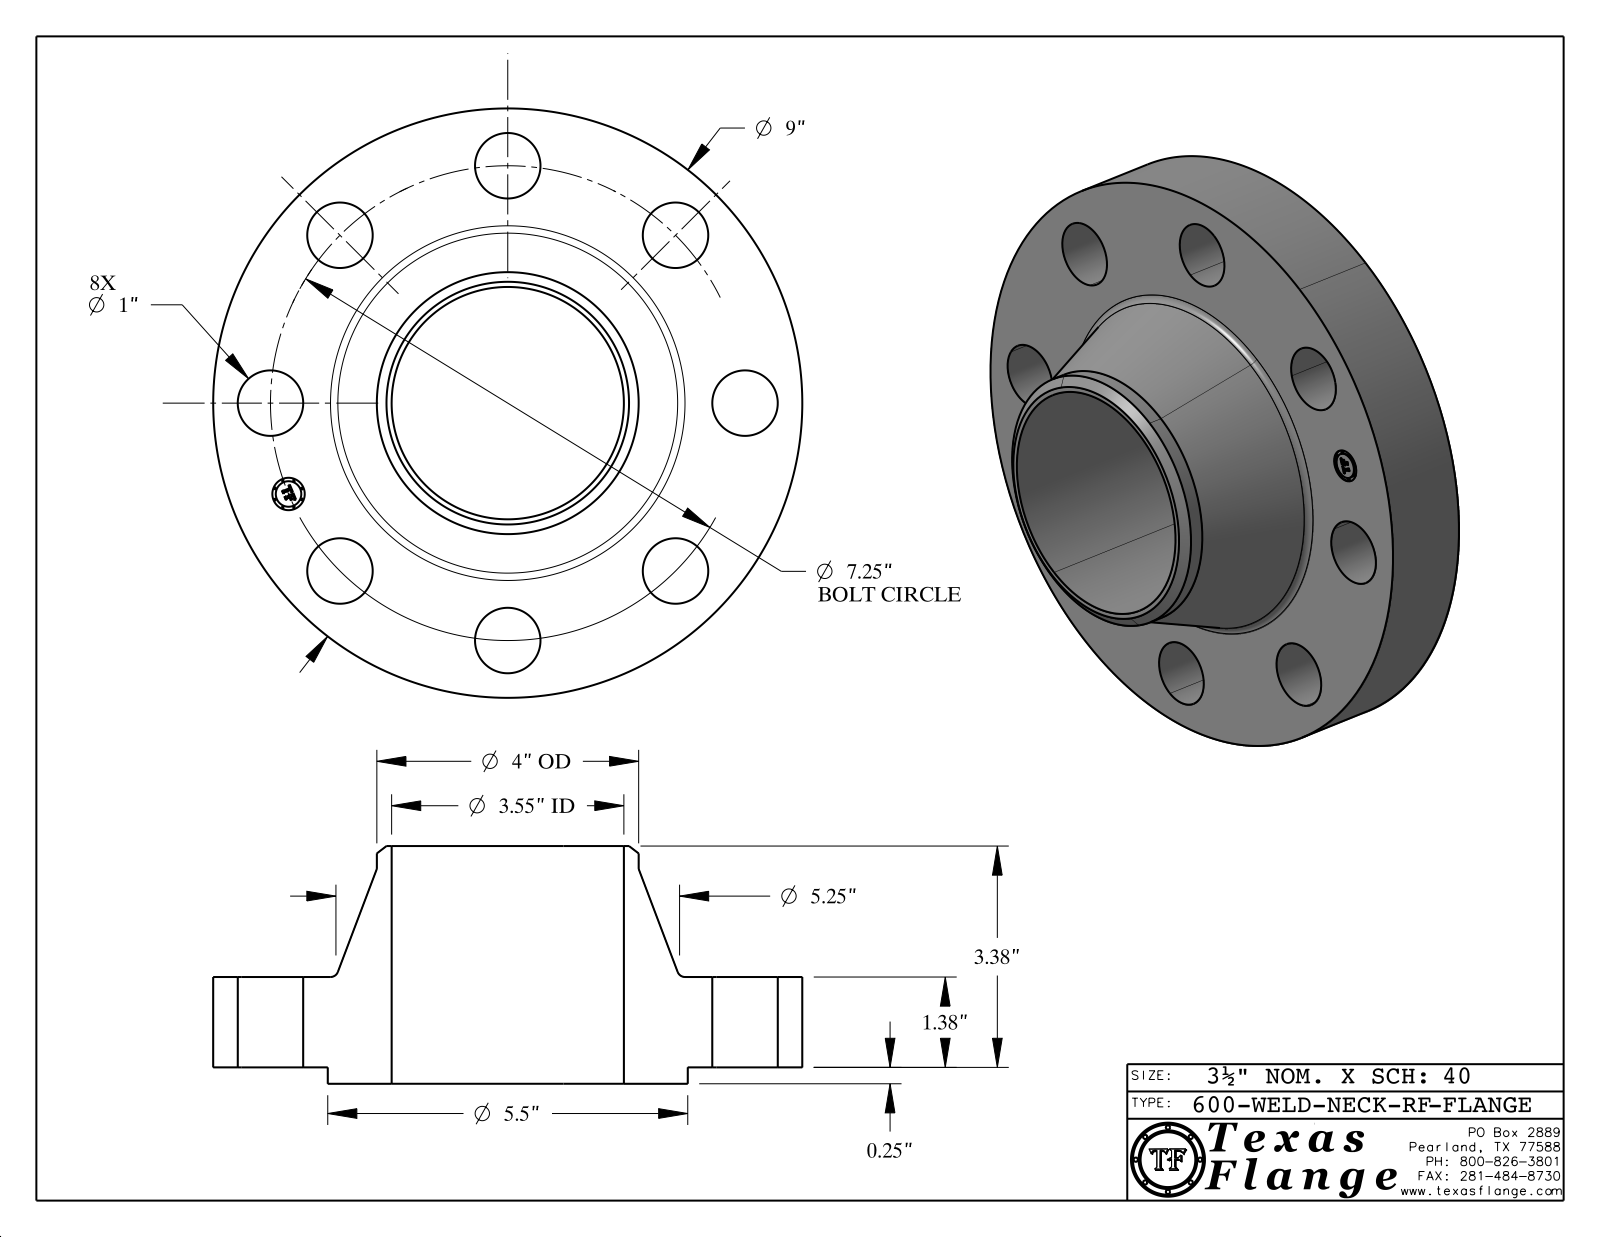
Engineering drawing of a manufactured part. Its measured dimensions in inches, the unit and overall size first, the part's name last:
Units: inches
Overall size (bounding box): 9 × 9 × 3.63
Round holes (diameter × count): ⌀1 ×8, ⌀0.495 ×1, ⌀3.548 ×1
Round bosses / shafts (diameter × count): ⌀0.03 ×8, ⌀9 ×1, ⌀5.5 ×1, ⌀4 ×1, ⌀0.39 ×1
Main face-to-face distances: 1.38, 0.25, 1.63, 3.63, 3.38, 2, 1.615, 1.365, 0.015, 2.015
Hole centre spacings: 3.625, 2.774, 5.127, 6.698, 7.25, 1.415, 7.111, 4.028
Volume: 81.38 in³ · Surface area: 233.1 in²
Bodies: 1 solid, 419 faces (369 planar, 44 cylindrical, 6 other)
Part name (STEP PRODUCT): 600-WELD-NECK-RF
STEP written by: CATIA V5 STEP AP214 (AUTOMOTIVE_DESIGN)
